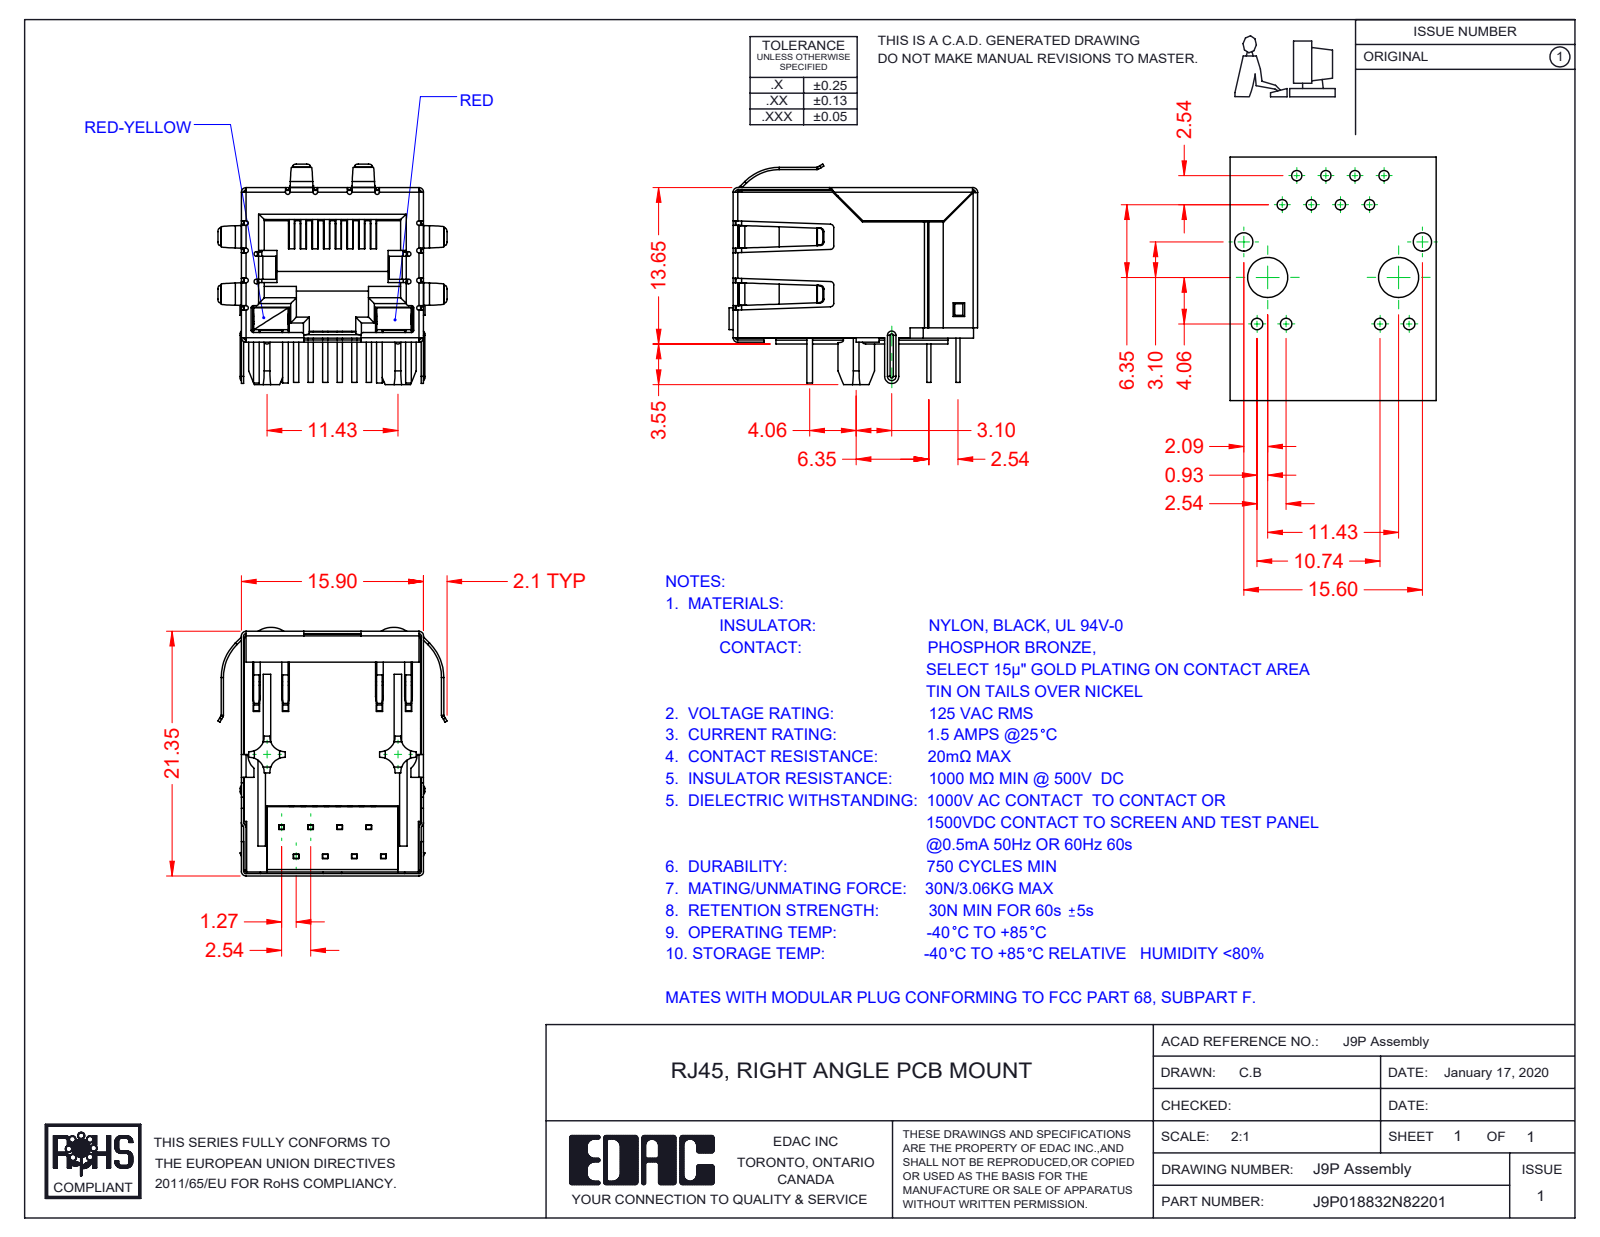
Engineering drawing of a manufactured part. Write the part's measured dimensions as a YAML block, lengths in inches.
part_name: "9P-LED Contacts; 9P-LED LED RH_2-Red; 9P-LED LED LH_8-Red-Yellow; J9P018832N82202 (+4 more)"
step_written_by: "SolidWorks 2016 (CONFIG_CONTROL_DESIGN)"
units: inches
bodies: {solids: 13, faces: 1474, planar: 1042, cylindrical: 338, other: 94}
overall_size: [0.854, 0.787, 0.758]
volume: 0.164
surface_area: 11.65
partial_cylinders:
  - {radius: 0.008, count: 39}
  - {radius: 0.02, count: 22}
  - {radius: 0.012, count: 20}
  - {radius: 0.016, count: 16}
  - {radius: 0.051, count: 8}
  - {radius: 0.009, count: 5}
  - {radius: 0.004, count: 4}
  - {radius: 0.012, count: 4}
face_to_face_distances: [0.608, 0.618, 0.616, 0.014, 0.021, 0.61, 0.487, 0.024, 0.055, 0.023]
